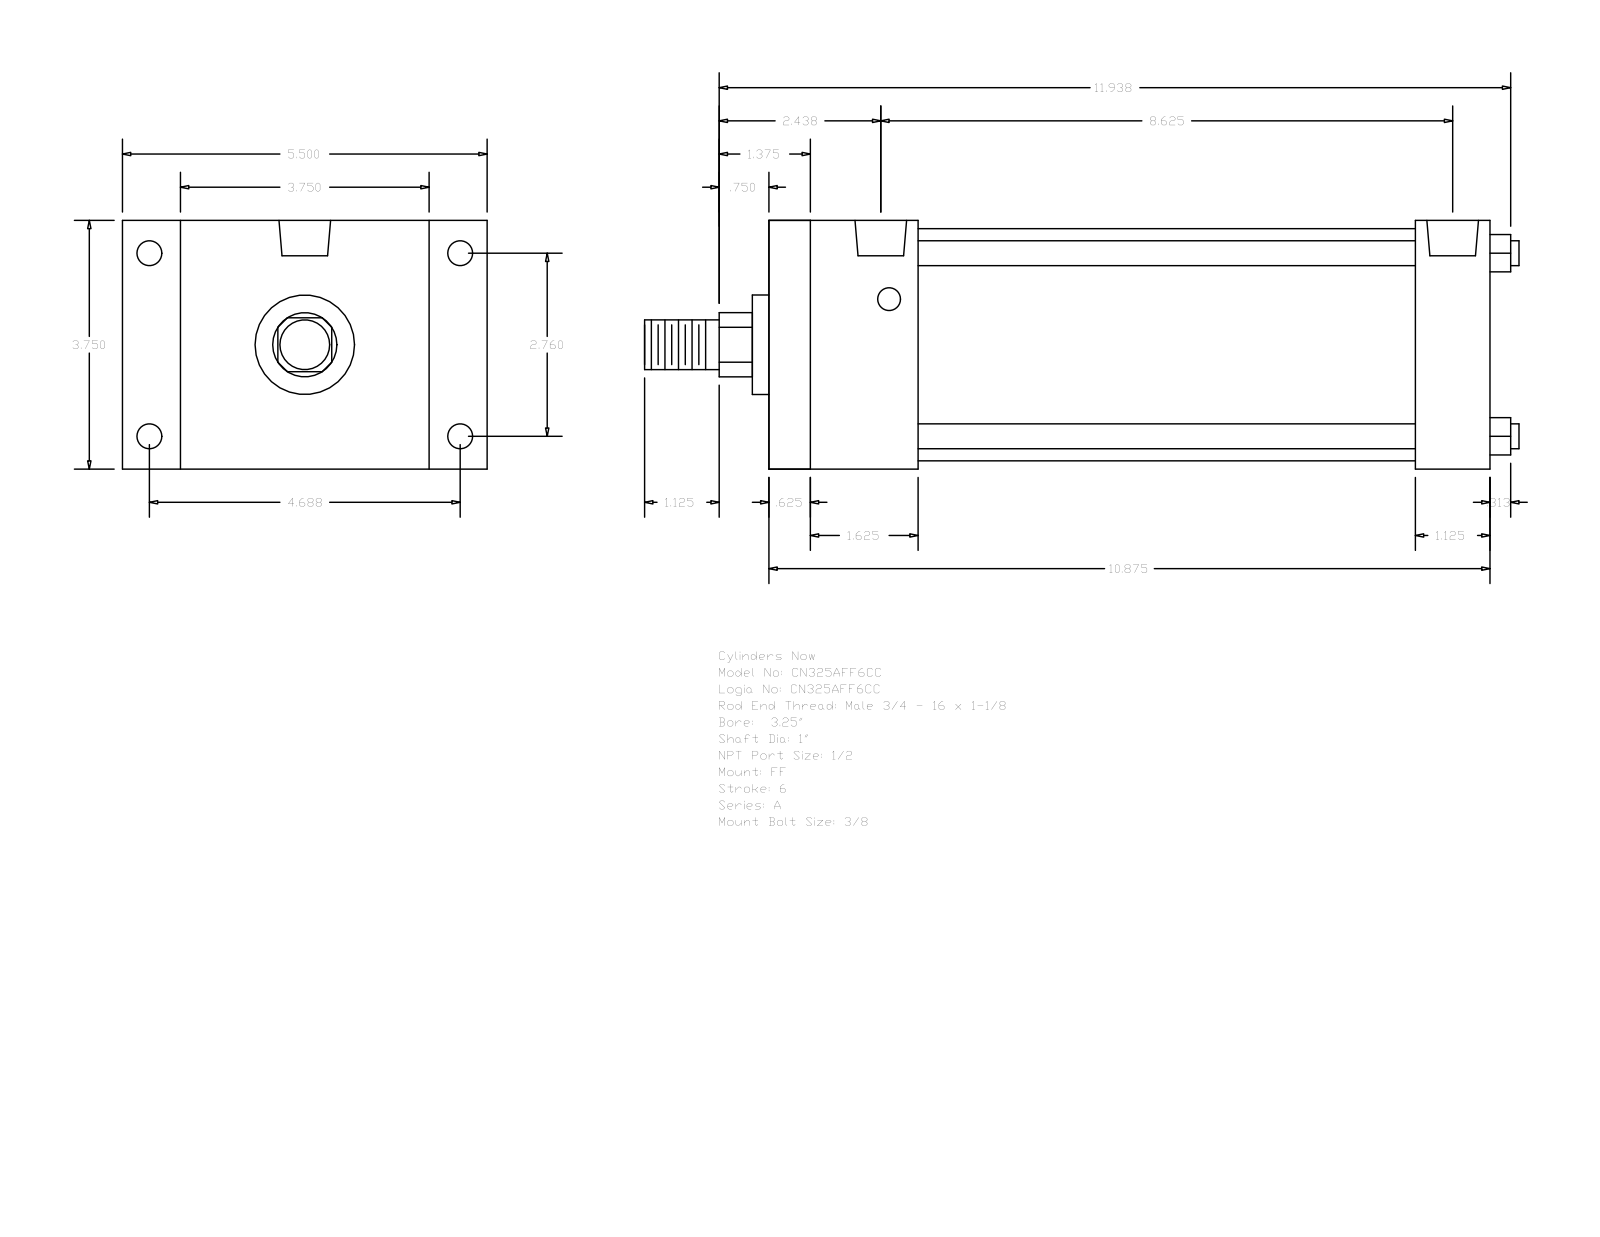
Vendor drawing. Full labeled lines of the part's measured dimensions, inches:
Part name (STEP PRODUCT): A_FF__0325_1
STEP written by: GSSL Pune (CONFIG_CONTROL_DESIGN)
Units: inches
Bodies: 0 solids, 92 faces (64 planar, 28 cylindrical, 0 other)
Overall size (bounding box): 13.187 × 5.5 × 3.75
Round holes (diameter × count): ⌀0.344 ×4, ⌀0.375 ×4, ⌀0.778 ×2
Round bosses / shafts (diameter × count): ⌀0.375 ×4, ⌀3.5 ×1, ⌀1.5 ×1, ⌀1 ×1, ⌀0.75 ×1
Partial cylindrical surfaces — rounded edges, fillets, slot ends (radius × count): R0.484 ×1
Main face-to-face distances: 3.75, 10.875, 0.625, 10.25, 0.875, 4.625, 1.125, 2.25, 9.75, 1.625
Hole centre spacings: 0.125, 2.76, 4.687, 5.439, 8.375, 8.5, 8.625
